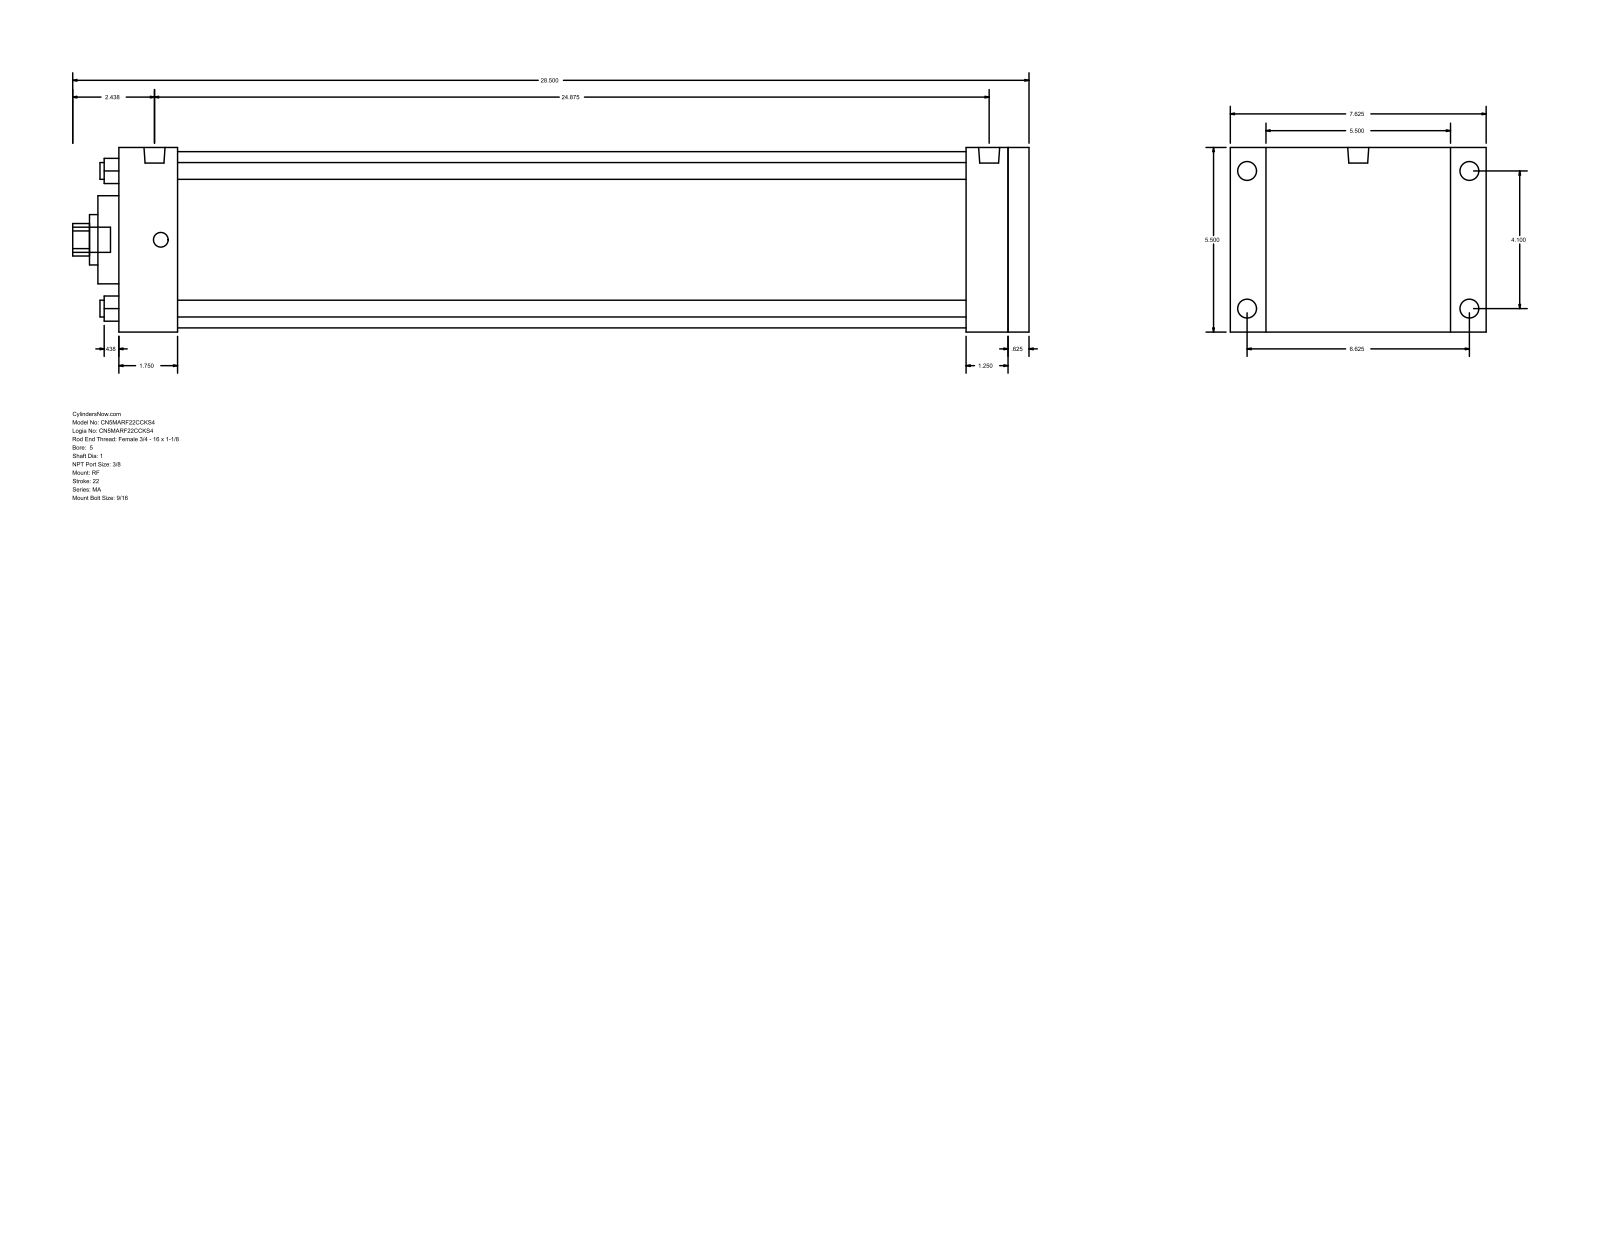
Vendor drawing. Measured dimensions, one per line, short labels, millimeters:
name: MA_RF__0500_1
written by: GSSL Pune (CONFIG_CONTROL_DESIGN)
unit: mm
bodies: 0 solids, 94 faces (65 planar, 29 cylindrical, 0 other)
size: 723.9 × 193.68 × 139.7
holes: 4× ⌀12.7, 1× ⌀25.4, 1× ⌀38.1, 1× ⌀66.67, 1× ⌀133.35
bosses: 4× ⌀14.29, 4× ⌀11.11, 2× ⌀15.93, 1× ⌀19.05
rounds: 1× R12.29
face distances: 139.7, 688.98, 673.1, 15.88, 44.46, 628.64, 644.52, 641.35, 596.89, 31.75
hole spacings: 73.64, 104.14, 147.28
